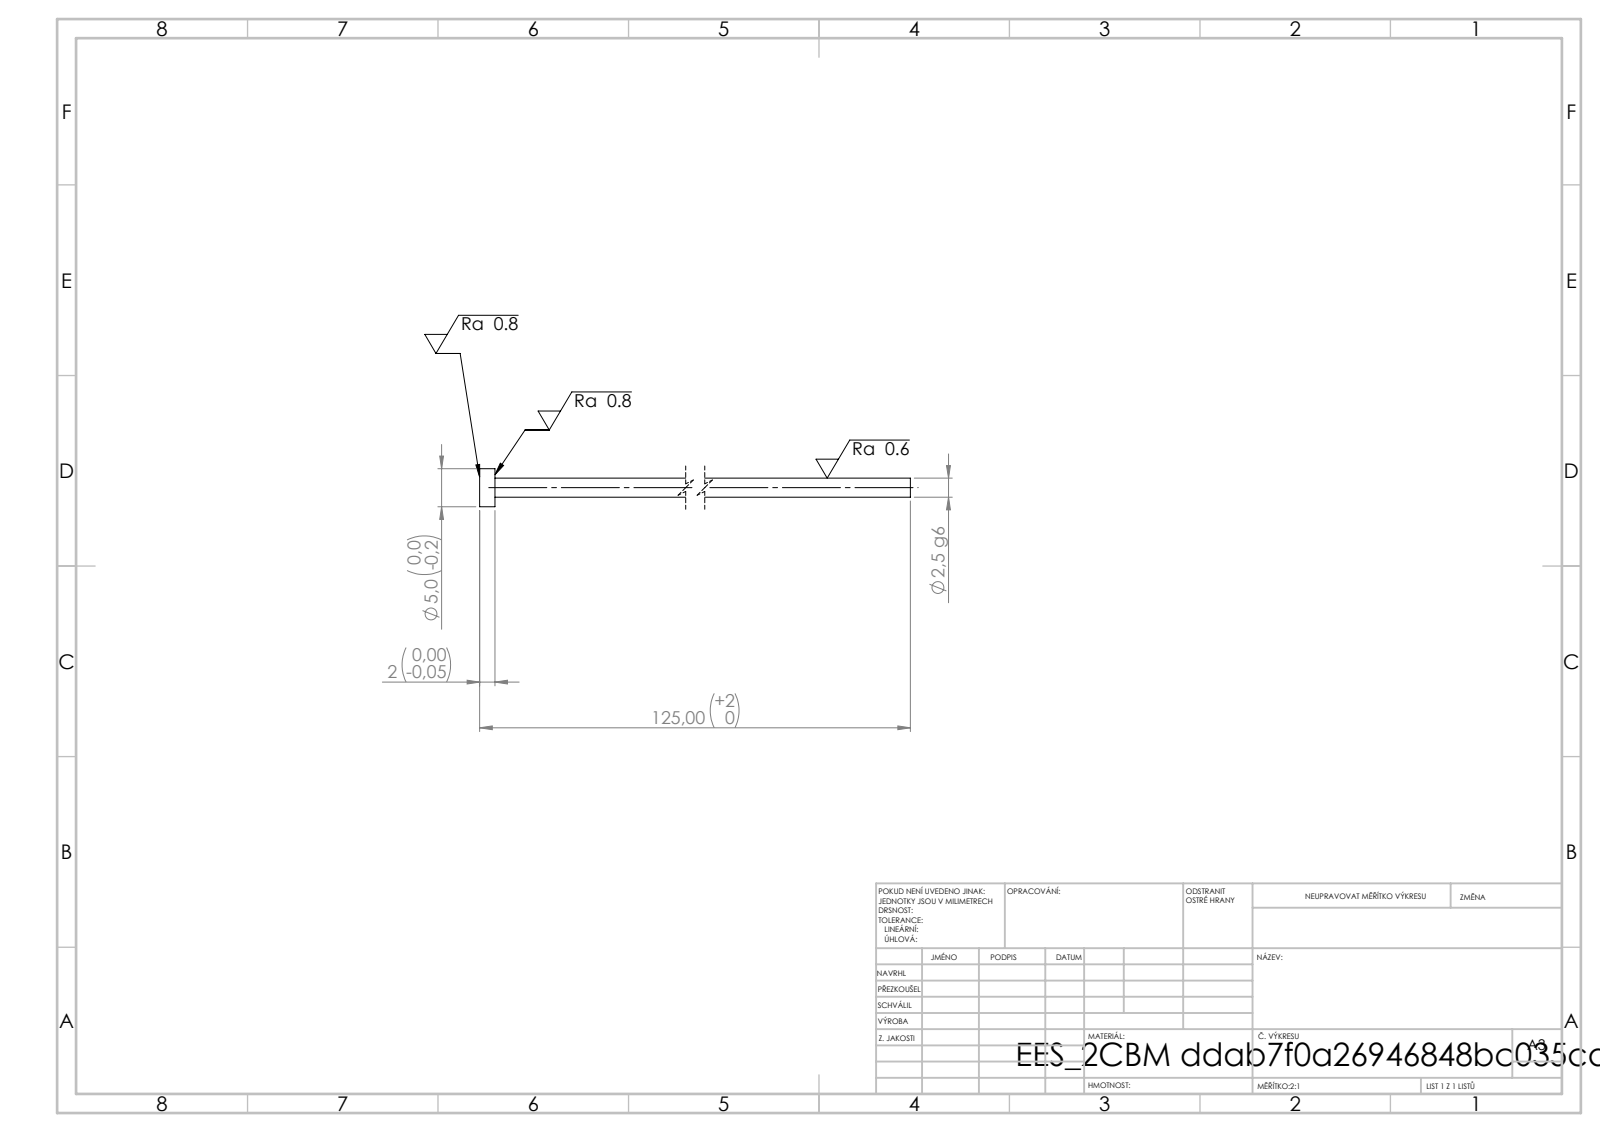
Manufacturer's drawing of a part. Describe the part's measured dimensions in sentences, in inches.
Its 3-D file was written by "SolidWorks 2019 (CONFIG_CONTROL_DESIGN)". It is 1 solid with 7 faces: 3 planar, 4 cylindrical and 0 other. Overall it measures 4.921 by 0.197 by 0.197 inches. Its volume is 0.039 cubic inches and its surface area 1.607 square inches. Round bosses or shafts: 1 of diameter 0.197, 1 of diameter 0.098. The main face-to-face distances are 0.079, 4.921, 4.843.
